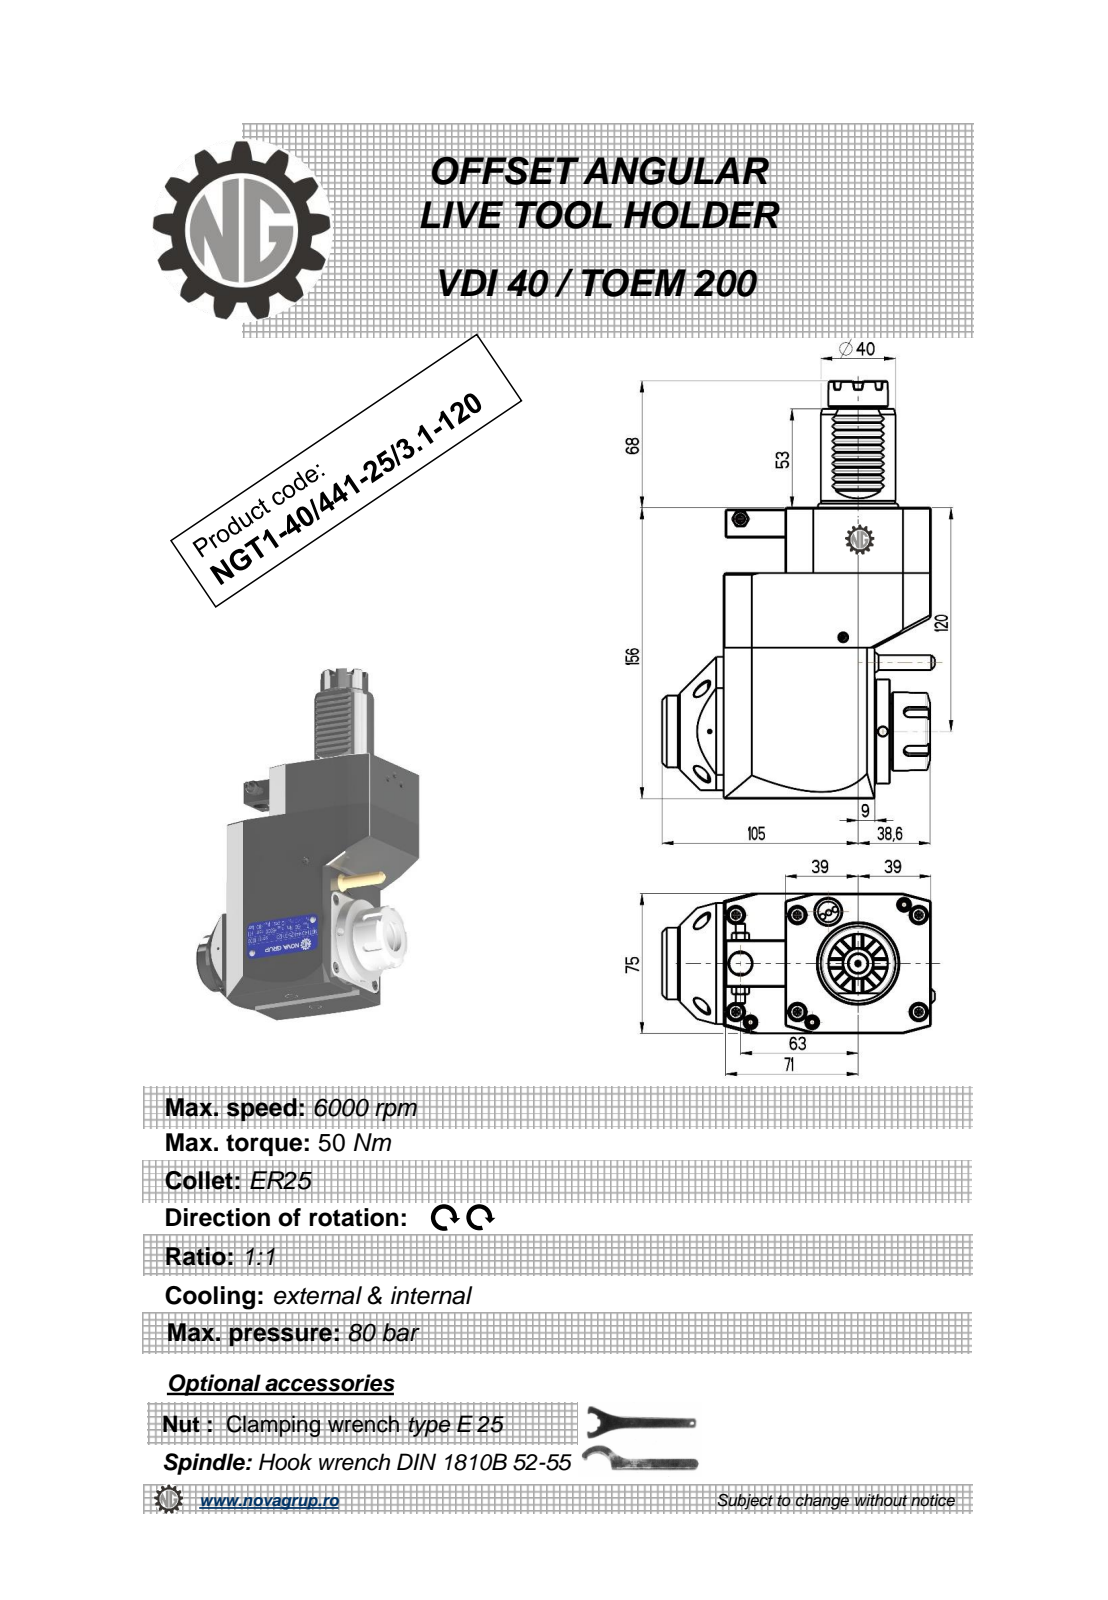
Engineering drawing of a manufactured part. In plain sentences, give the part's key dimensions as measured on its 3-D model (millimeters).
The part is named "NGT1_40_441_25_3_1_120". Its 3-D file was written by "PRO/ENGINEER BY PARAMETRIC TECHNOLOGY CORPORATION, 2010280 (CONFIG_CONTROL_DESIGN)". It is 1 solid with 513 faces: 242 planar, 83 cylindrical and 188 other. Overall it measures 224 by 146.14 by 75 millimeters. Its volume is 1 204 000 cubic millimeters and its surface area 90 411 square millimeters. Round holes: 3 of diameter 5, 1 of diameter 3, 1 of diameter 9.5, 1 of diameter 12, 1 of diameter 20.3. Round bosses or shafts: 1 of diameter 56, 1 of diameter 43, 1 of diameter 42, 1 of diameter 40, 1 of diameter 38.5, 1 of diameter 33, 1 of diameter 32, 1 of diameter 17.2. Partial cylindrical surfaces (rounded edges, fillets, slot ends): 12 of radius 0.26, 10 of radius 0.3, 6 of radius 0.2, 5 of radius 3, 1 of radius 0.5, 1 of radius 40. The main face-to-face distances are 75, 156, 111, 33, 35, 121, 81, 30, 78, 48. The hole center spacings are 40.93, 76.25, 77.5, 112.5.
